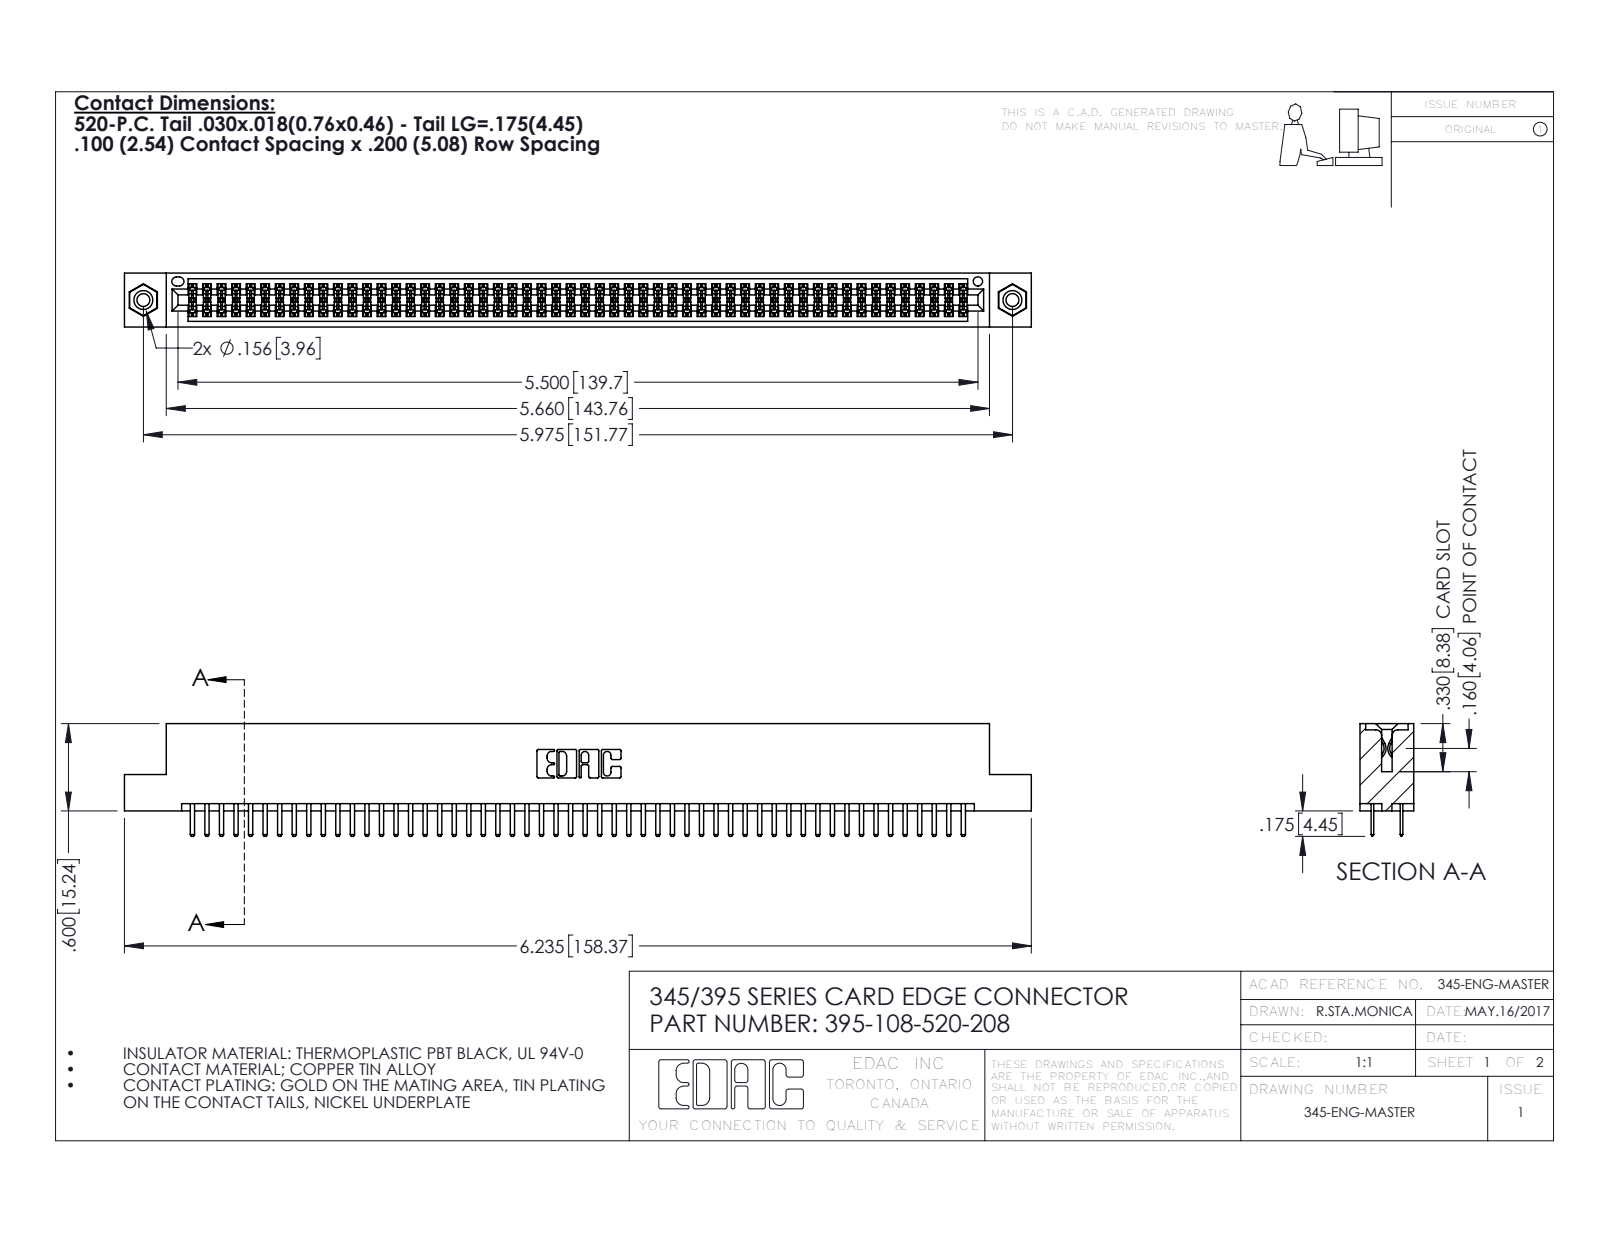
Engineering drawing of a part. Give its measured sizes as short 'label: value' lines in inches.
name: 345-250-001_345-250-003-102; 395-108-520-208; 345 Part_Flush Mounting Lugs - 0.156 Dia-TI; 345-292-001_345-293-120
written by: SolidWorks 2016 (CONFIG_CONTROL_DESIGN)
unit: in
bodies: 111 solids, 6018 faces (3892 planar, 2110 cylindrical, 16 other)
size: 6.235 × 0.775 × 0.37
volume: 0.942 in³; area: 35.6 in²
holes: 2× ⌀0.089, 2× ⌀0.125, 2× ⌀0.156, 1× ⌀0.064
bosses: 2× ⌀0.155
rounds: 162× R0.006, 112× R0.01, 22× R0.01, 6× R0.007, 6× R0.031, 3× R0.026, 2× R0.014, 2× R0.019
face distances: 0.072, 0.298, 0.2, 0.37, 0.098, 0.272, 0.025, 0.225, 0.022, 0.072
hole spacings: 0.27, 5.739, 5.975
